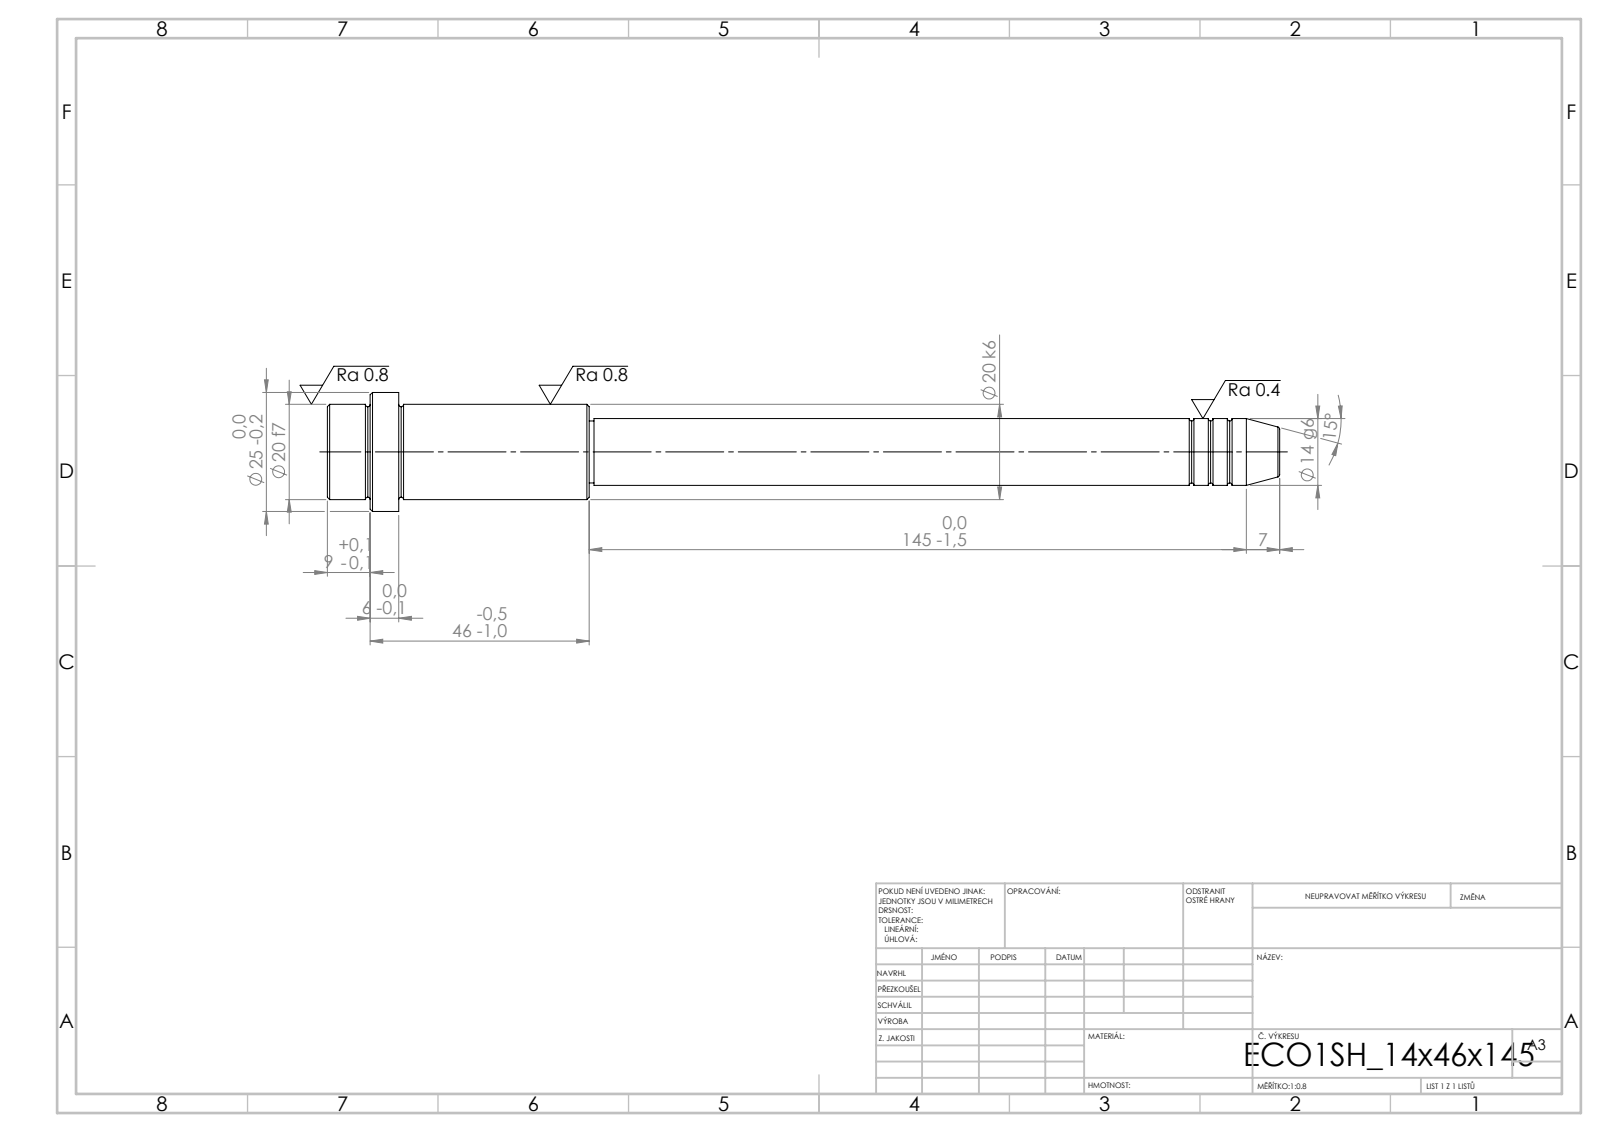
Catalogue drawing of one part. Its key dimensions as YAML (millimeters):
step_written_by: "SolidWorks 2019 (CONFIG_CONTROL_DESIGN)"
units: millimeters
bodies: {solids: 1, faces: 52, planar: 6, cylindrical: 16, other: 30}
overall_size: [200, 25, 25]
volume: 40251
surface_area: 10912
round_bosses_or_shafts:
  - {diameter: 25, count: 1}
  - {diameter: 20, count: 1}
  - {diameter: 14, count: 1}
  - {diameter: 13, count: 1}
face_to_face_distances: [15, 40, 55, 46, 6, 9, 145, 185, 191, 200]
